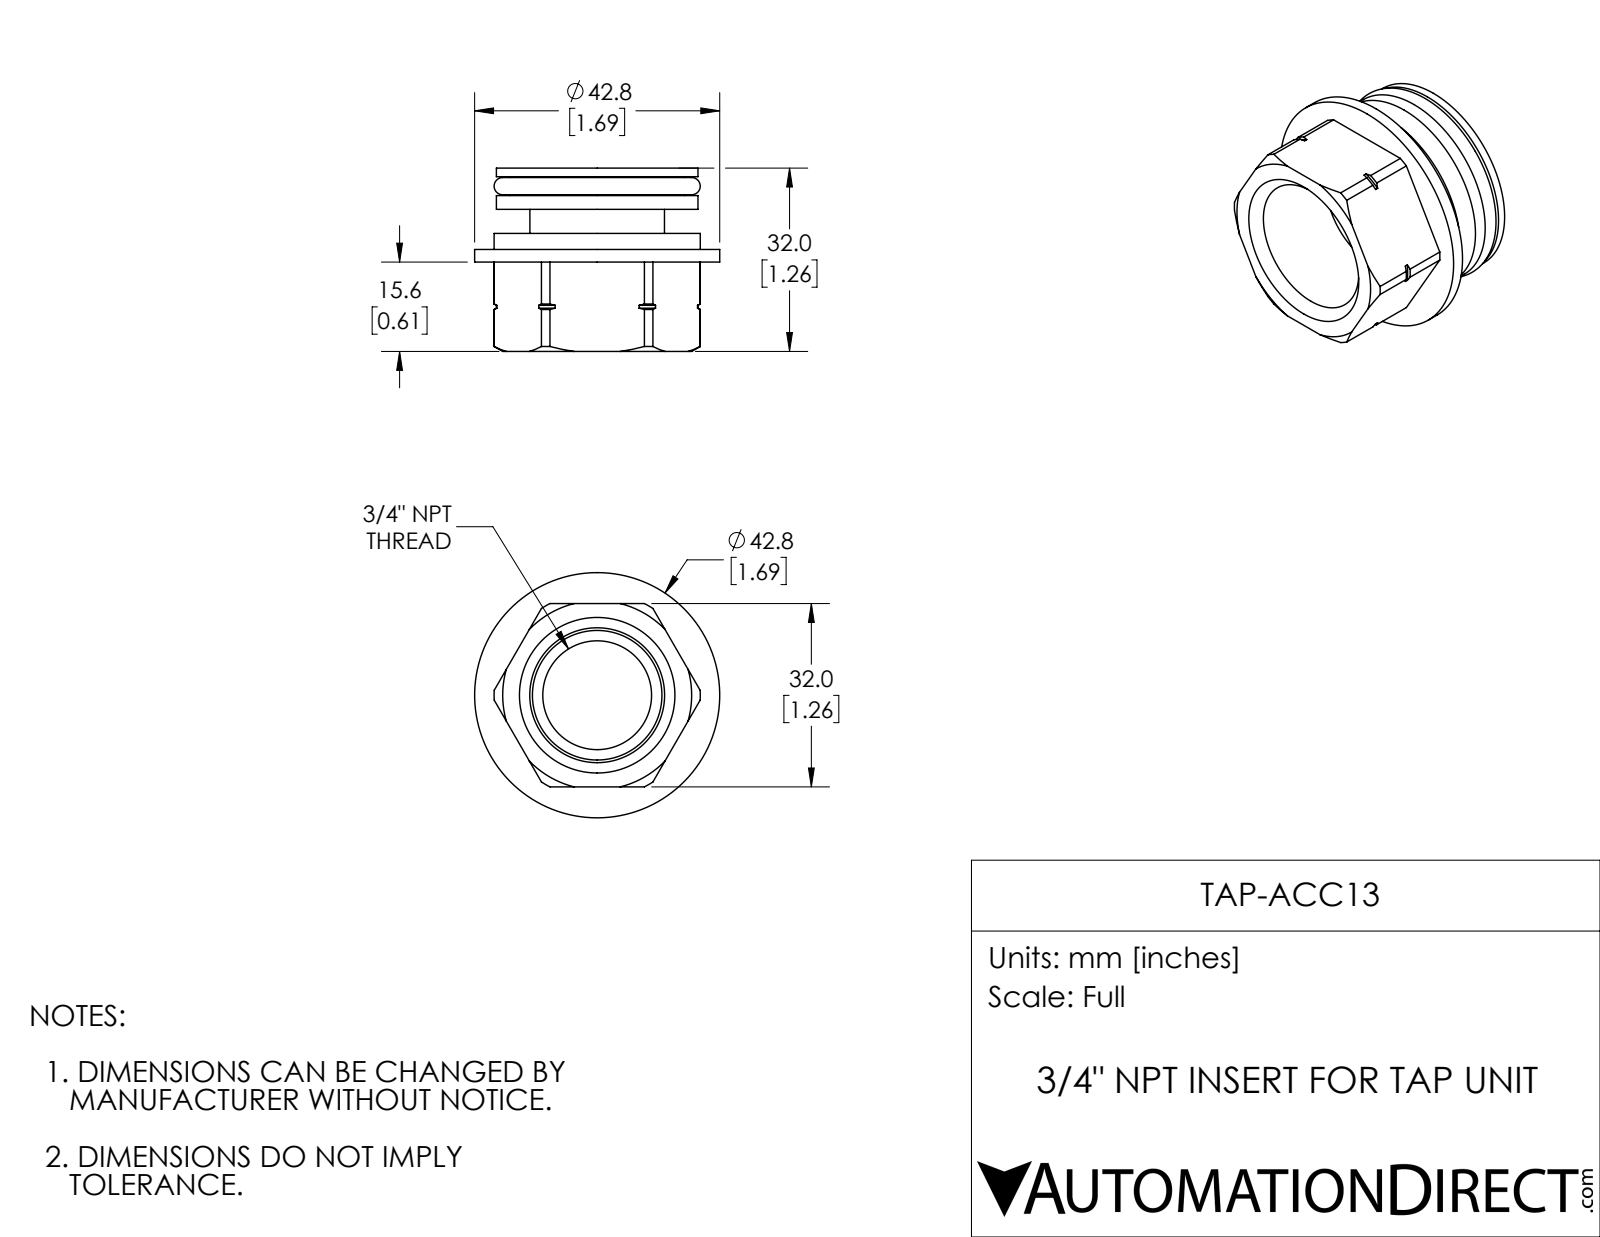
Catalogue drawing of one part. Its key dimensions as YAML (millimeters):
part_name: "TAP-ACC13"
step_written_by: "SolidWorks 2017 (AUTOMOTIVE_DESIGN)"
units: millimeters
bodies: {solids: 1, faces: 82, planar: 14, cylindrical: 36, other: 32}
overall_size: [42.8, 42.8, 32]
volume: 16100
surface_area: 9800
round_holes:
  - {diameter: 19, count: 1}
  - {diameter: 26, count: 1}
round_bosses_or_shafts:
  - {diameter: 42.8, count: 1}
  - {diameter: 36, count: 1}
  - {diameter: 35.2, count: 1}
  - {diameter: 30.5, count: 1}
  - {diameter: 23.5, count: 1}
face_to_face_distances: [32, 5, 9.2, 4.2, 16.4, 11.4, 7.2, 2.2, 2.8, 7]
